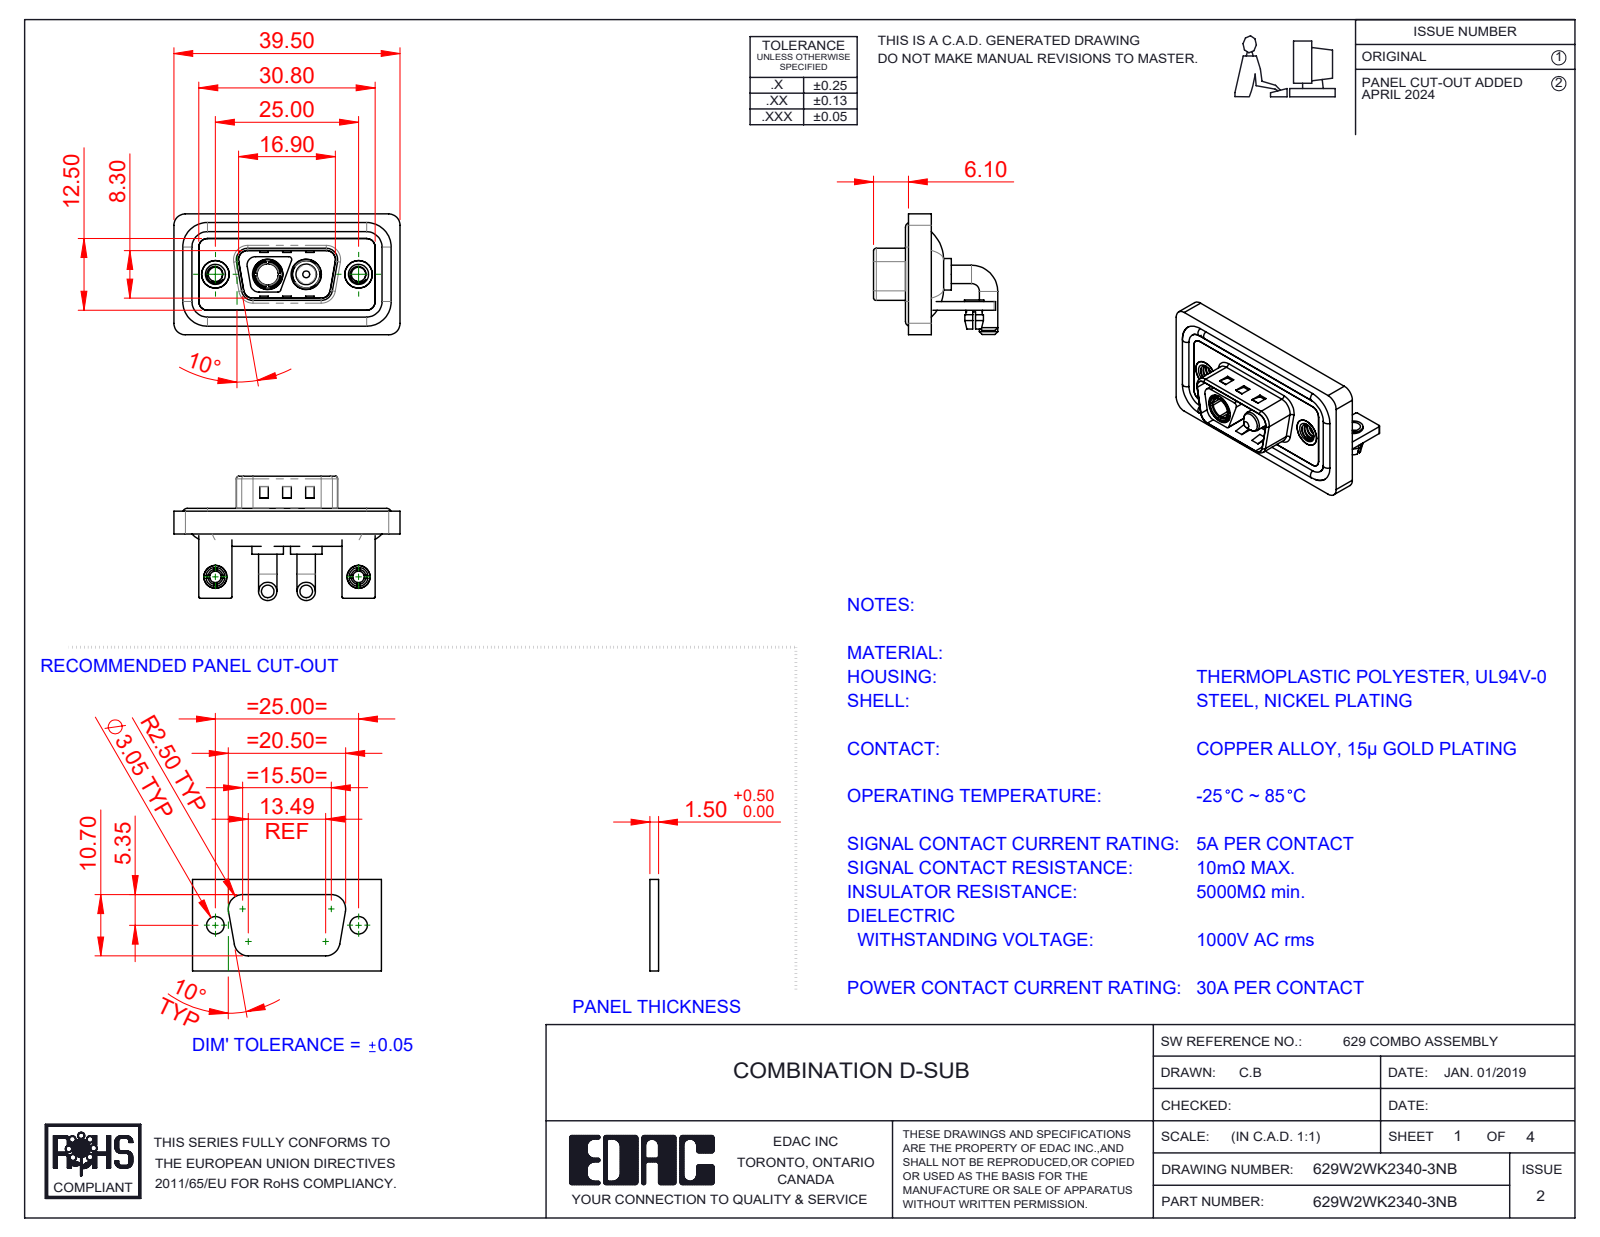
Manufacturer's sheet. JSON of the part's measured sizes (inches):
{"part_name": "Power Pin_30A RA; 629Combo Shell Front_09 Contacts; 629Combo Waterproof Housing_09 Contacts; 629Combo Shell Rear_09 Contacts (+6 more)", "step_written_by": "SolidWorks 2023 (CONFIG_CONTROL_DESIGN)", "units": "inches", "bodies": {"solids": 15, "faces": 672, "planar": 257, "cylindrical": 281, "other": 134}, "overall_size": [1.555, 0.854, 0.831], "volume_in3": 0.308, "surface_area_in2": 12.97, "round_holes": [[0.098, 4], [0.079, 2], [0.126, 2], [0.157, 2], [0.189, 2], [0.191, 2], [0.197, 2], [0.209, 2], [0.146, 1]], "round_bosses_or_shafts": [[0.126, 4], [0.063, 4], [0.217, 2], [0.205, 2], [0.193, 2], [0.187, 2], [0.157, 2], [0.148, 2]], "partial_cylinders_radius": [[0.059, 20], [0.079, 19], [0.01, 16], [0.02, 11], [0.063, 8], [0.024, 4], [0.026, 4], [0.035, 4]], "face_to_face_distances": [0.016, 0.059, 0.114, 0.031, 0.043, 0.047, 0.083, 0.063, 0.146, 0.098], "hole_center_spacings": [0.36, 0.624, 0.984, 0.265]}
